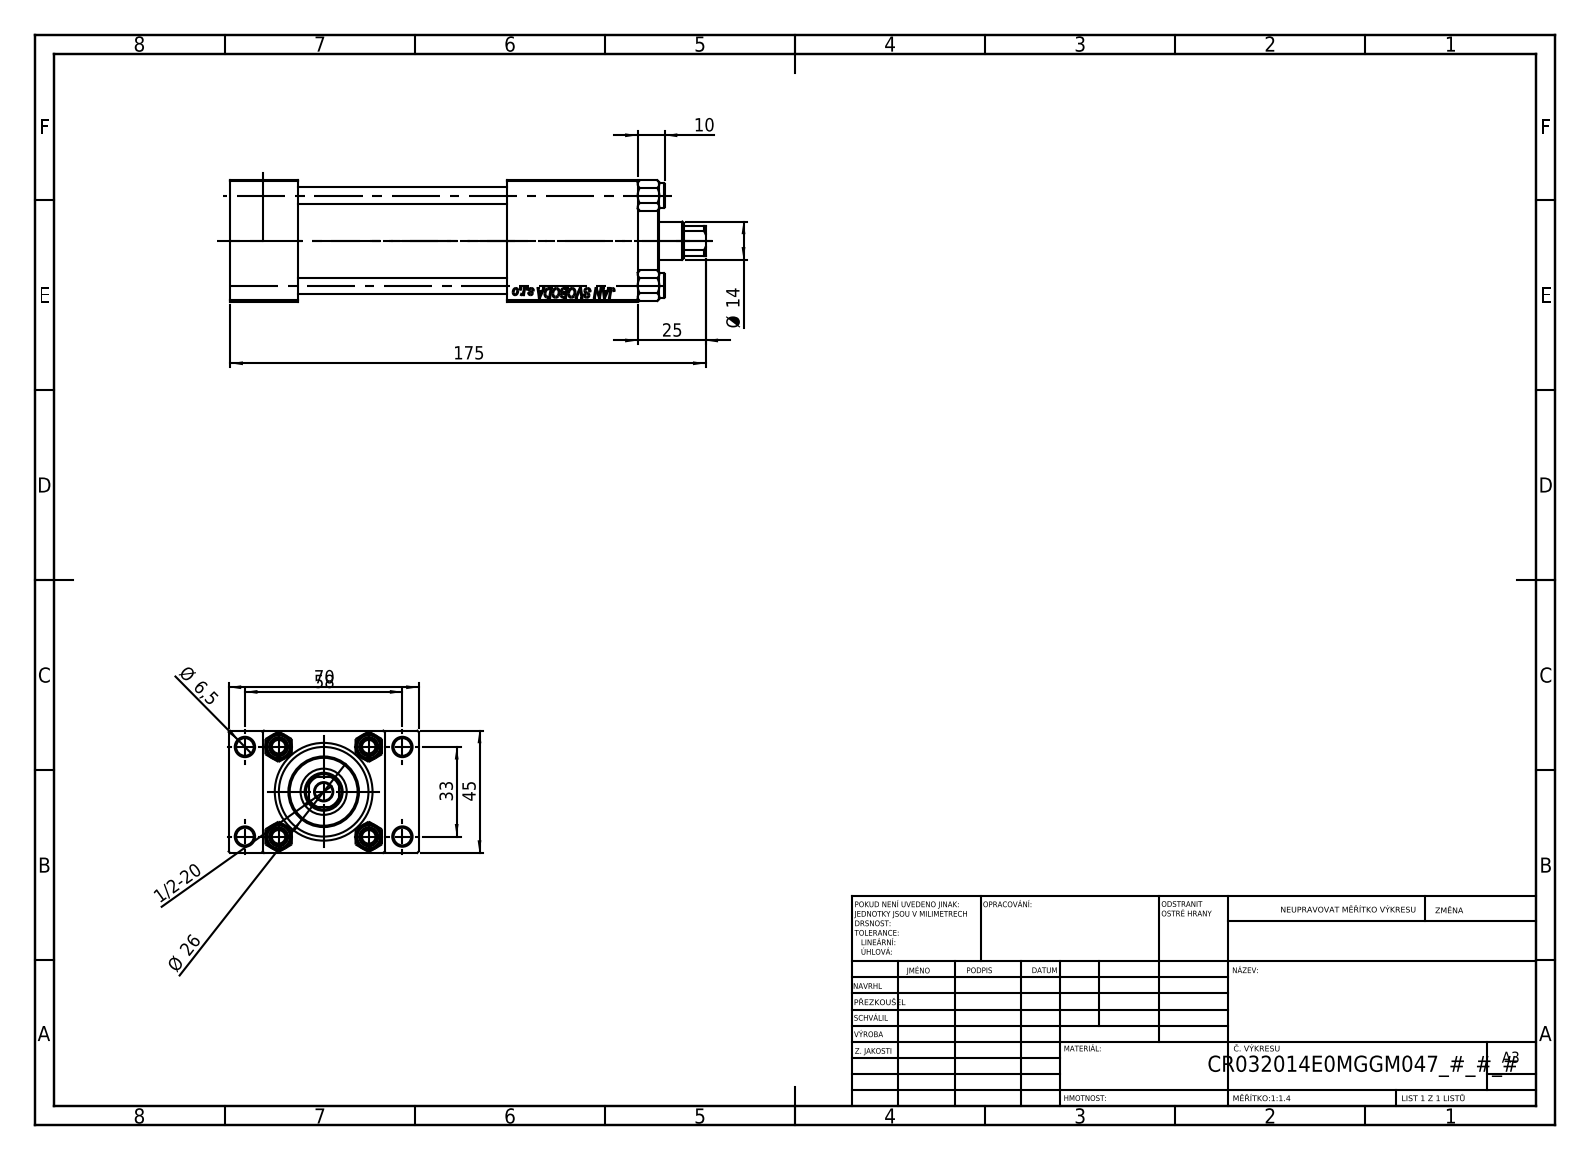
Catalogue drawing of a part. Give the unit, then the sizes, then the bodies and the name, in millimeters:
Units: millimetres
Overall size (bounding box): 175 × 70 × 45
Round holes (diameter × count): ⌀6.5 ×5, ⌀6 ×4, ⌀7 ×2, ⌀13.16 ×2, ⌀20 ×2, ⌀14 ×1, ⌀17 ×1, ⌀24 ×1, ⌀32 ×1, ⌀33 ×1
Round bosses / shafts (diameter × count): ⌀9 ×4, ⌀38 ×1, ⌀26 ×1
Partial cylindrical surfaces — rounded edges, fillets, slot ends (radius × count): R6.5 ×1
Main face-to-face distances: 45, 25, 12.5, 57.5, 150, 125, 70, 102, 77, 48
Hole centre spacings: 12.4, 23.48, 33.2, 33.37, 35.35, 45.6, 56.35, 33
Volume: 236 189 mm³ · Surface area: 85 234 mm²
Bodies: 11 solids, 1136 faces (497 planar, 87 cylindrical, 552 other)
Part name (STEP PRODUCT): V215CR_E_Body; V215CR_TYCINKA_E; V215CR_VCP_E; V215_VC_A (+1 more)
STEP written by: SolidWorks 2019 (CONFIG_CONTROL_DESIGN)
